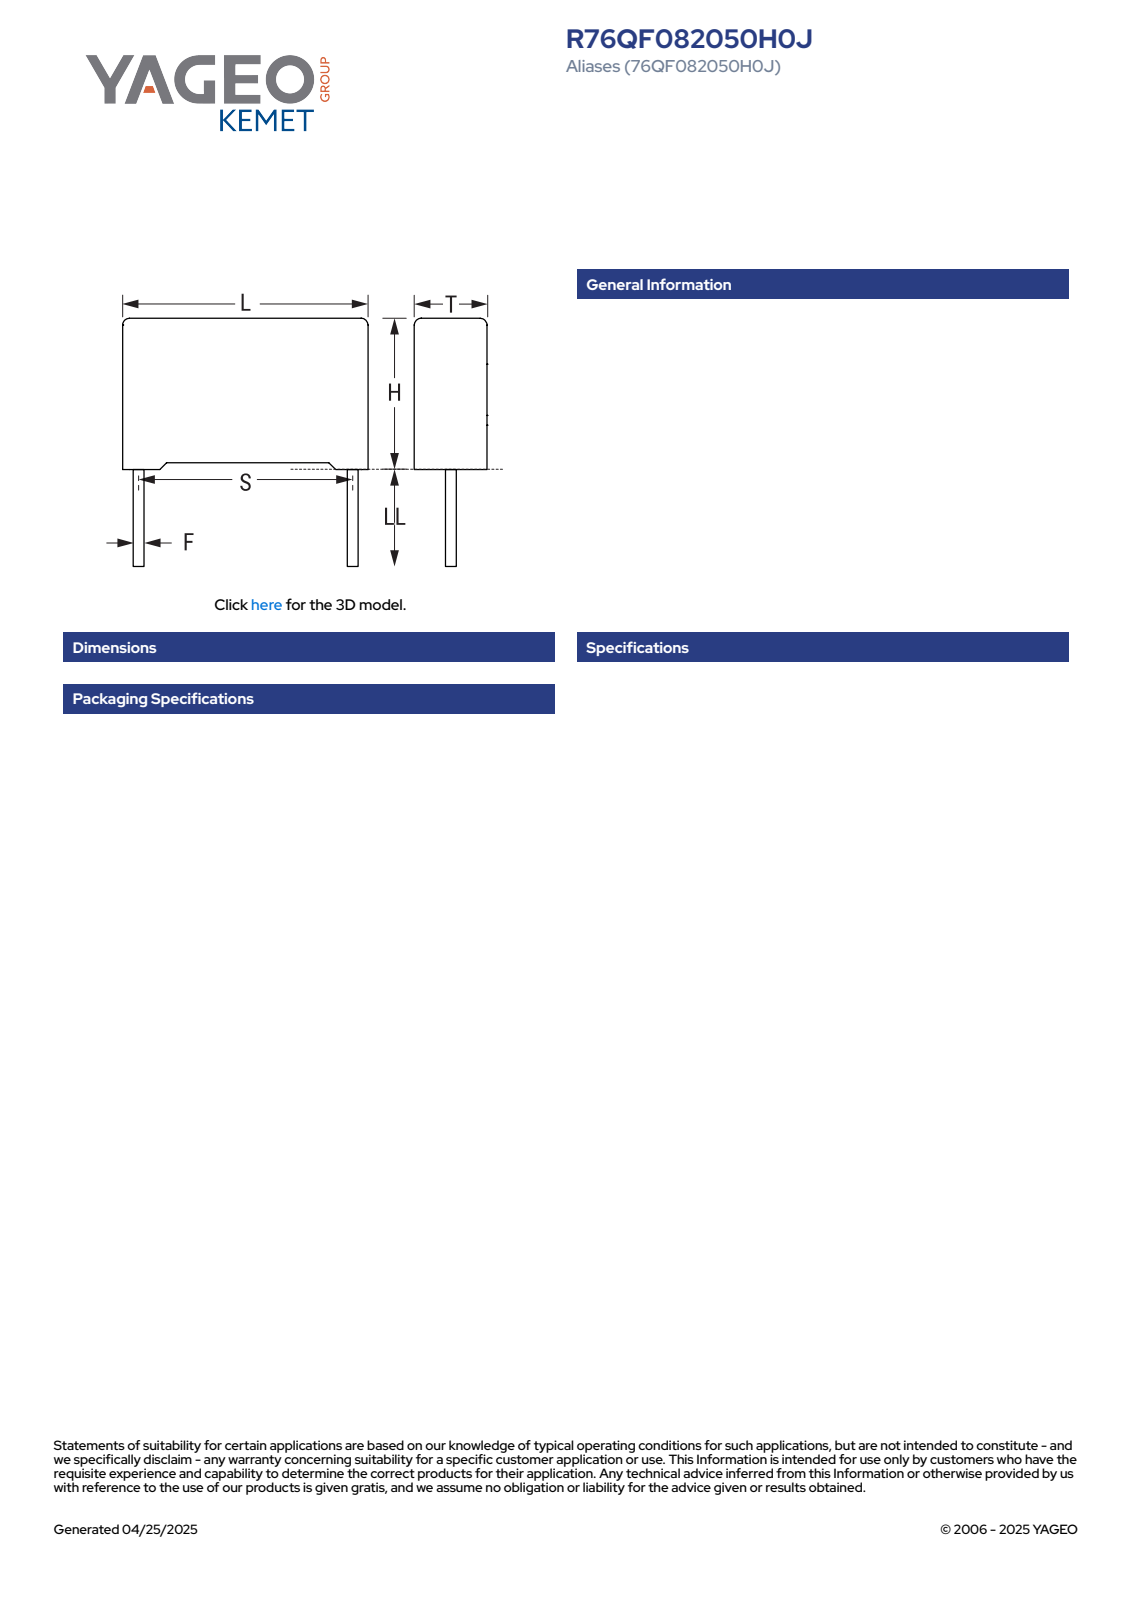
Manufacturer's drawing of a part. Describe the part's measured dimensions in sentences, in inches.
The part is named "CFR_RB2R76_13X9X4_L13.2H9.1T4.2S10LL27F0.65". Its 3-D file was written by "SolidWorks 2014 (AUTOMOTIVE_DESIGN)". It is 4 solids with 85 faces: 77 planar, 8 cylindrical and 0 other. Overall it measures 1.421 by 0.52 by 0.166 inches. Its volume is 0.03 cubic inches and its surface area 0.871 square inches. Round bosses or shafts: 2 of diameter 0.026. Partial cylindrical surfaces (rounded edges, fillets, slot ends): 4 of radius 0.02. The main face-to-face distances are 0.165, 0.329, 0.52, 0.017, 0.148, 0.03, 0.358, 0.131, 0.012, 0.346.
